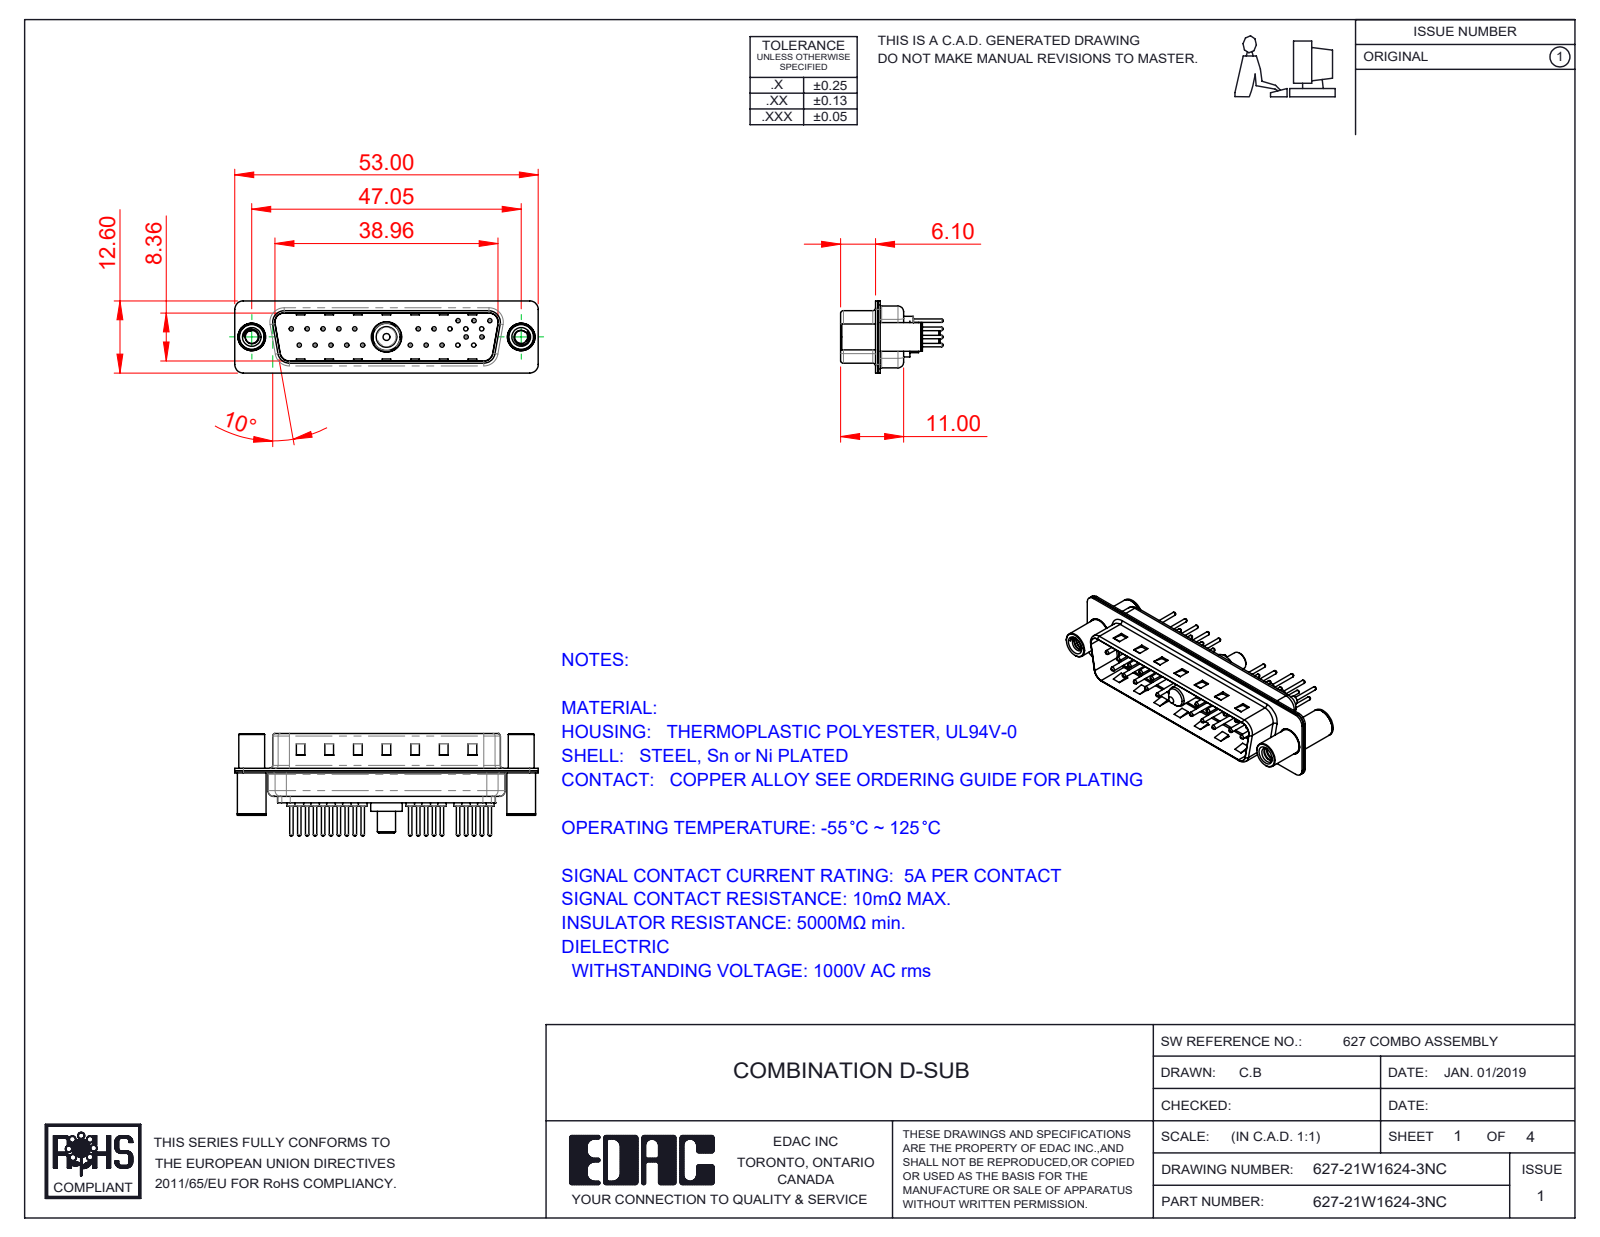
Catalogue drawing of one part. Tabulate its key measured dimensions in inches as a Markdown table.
| quantity | value |
| --- | --- |
| part name | Power Pin_30A S; 627Combo Contact Row 1_24; 627-21W1624-3NC; 627Combo Contact Row 2_24 (+5 more) |
| STEP written by | SolidWorks 2016 (CONFIG_CONTROL_DESIGN) |
| units | inches |
| bodies | 27 solids, 1251 faces (327 planar, 498 cylindrical, 426 other) |
| overall size | 2.087 × 0.705 × 0.496 |
| volume | 0.188 in³ |
| surface area | 11.41 in² |
| round holes (diameter × count) | 0.03 × 20, 0.063 × 20, 0.079 × 20, 0.089 × 2, 0.128 × 2, 0.157 × 2, 0.189 × 2, 0.191 × 1, 0.209 × 1 |
| round bosses / shafts (diameter × count) | 0.059 × 20, 0.024 × 20, 0.079 × 5, 0.03 × 5, 0.197 × 2, 0.193 × 2, 0.177 × 2, 0.217 × 1 |
| partial cylindrical surfaces (radius × count) | 0.059 × 16, 0.079 × 12, 0.02 × 8, 0.063 × 8, 0.01 × 4, 0.024 × 4, 0.026 × 4, 0.035 × 4 |
| main face-to-face distances | 0.016, 0.032, 0.377, 0.345, 0.059, 0.22, 0.236, 0.205, 0.048, 0.393 |
| hole center spacings | 0.124, 0.109, 0.218, 0.327, 0.198, 0.763, 0.826, 0.872 |
